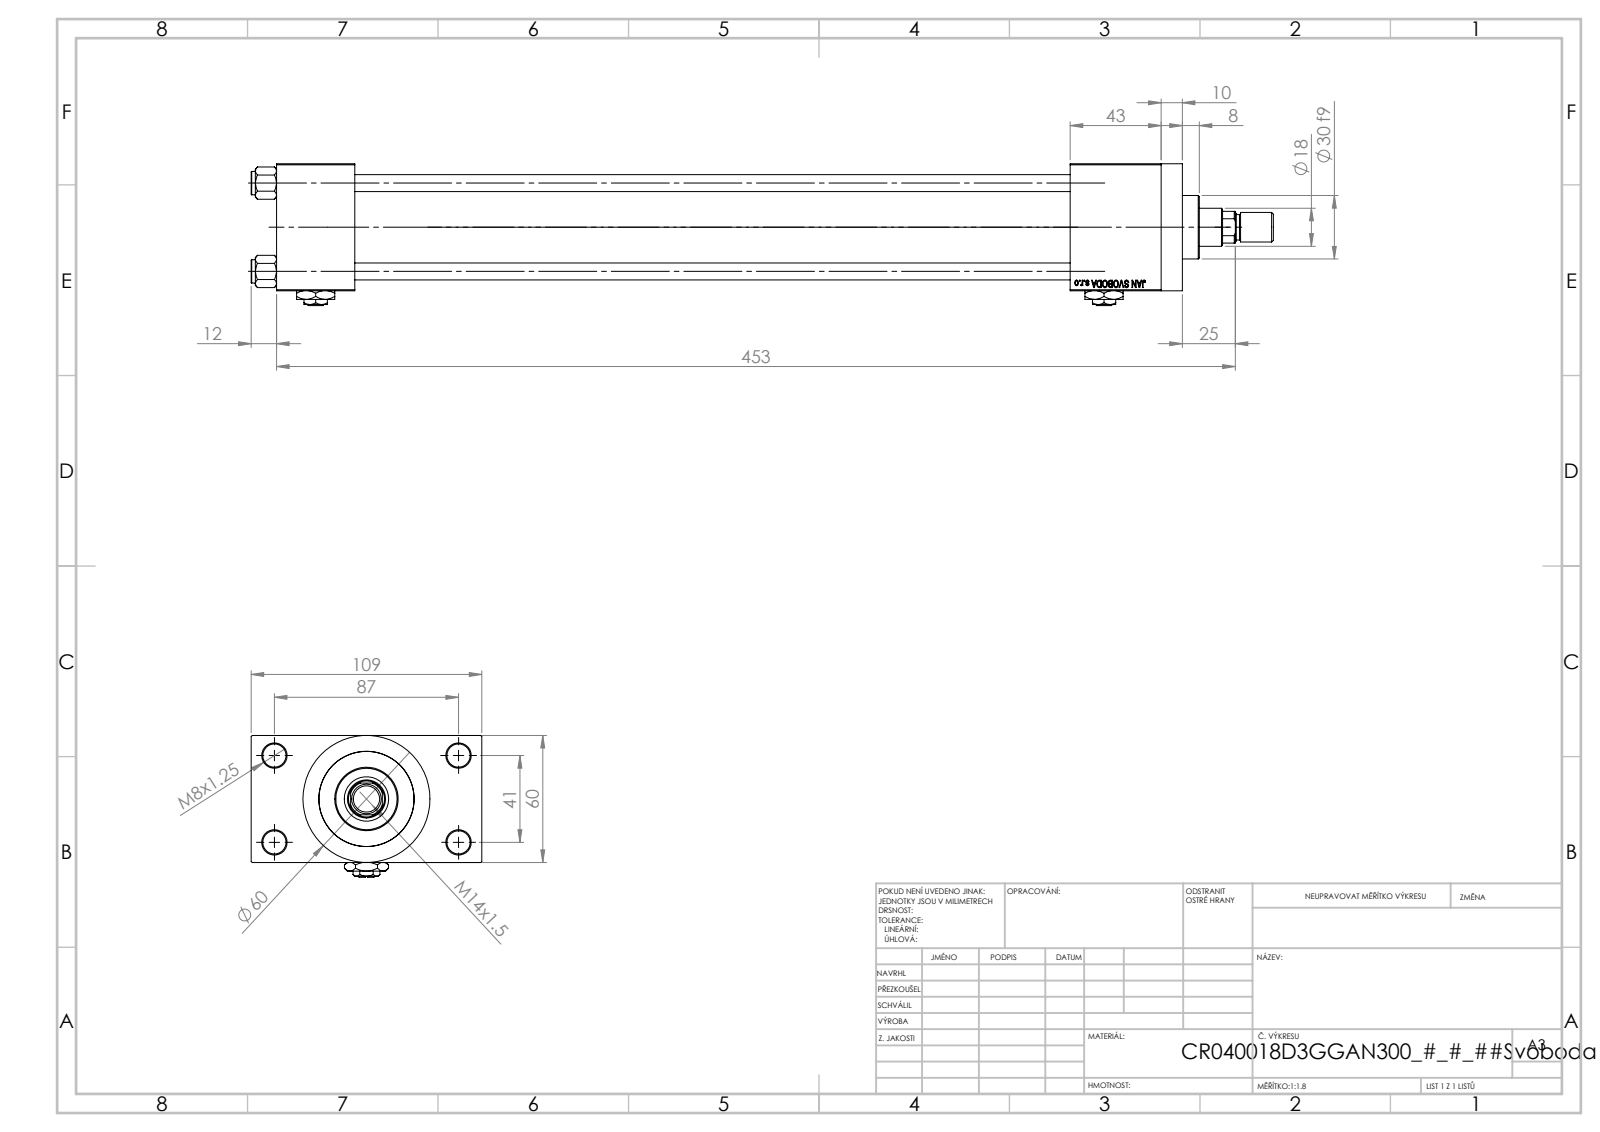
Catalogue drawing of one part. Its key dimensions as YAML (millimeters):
part_name: "V215CR_D_Body; V215CR_VCP_D; ROD_END_AH; V215_VC_A (+3 more)"
step_written_by: "SolidWorks 2019 (CONFIG_CONTROL_DESIGN)"
units: millimeters
bodies: {solids: 14, faces: 1220, planar: 550, cylindrical: 104, other: 566}
overall_size: [483, 109, 67]
volume: 759287
surface_area: 244673
round_holes:
  - {diameter: 8, count: 4}
  - {diameter: 11, count: 4}
  - {diameter: 7, count: 2}
  - {diameter: 16.66, count: 2}
  - {diameter: 24, count: 2}
  - {diameter: 8.5, count: 1}
  - {diameter: 18, count: 1}
  - {diameter: 21, count: 1}
  - {diameter: 31, count: 1}
  - {diameter: 40, count: 1}
  - {diameter: 45, count: 1}
round_bosses_or_shafts:
  - {diameter: 11, count: 4}
  - {diameter: 60, count: 1}
  - {diameter: 46, count: 1}
  - {diameter: 30, count: 1}
  - {diameter: 14, count: 1}
  - {diameter: 12, count: 1}
partial_cylinders:
  - {radius: 8.5, count: 1}
face_to_face_distances: [60, 24.5, 84.5, 338, 37, 375, 43, 418, 381, 109]
hole_center_spacings: [22.65, 29.49, 41.7, 47.15, 48.09, 64.35, 76.49, 41]
